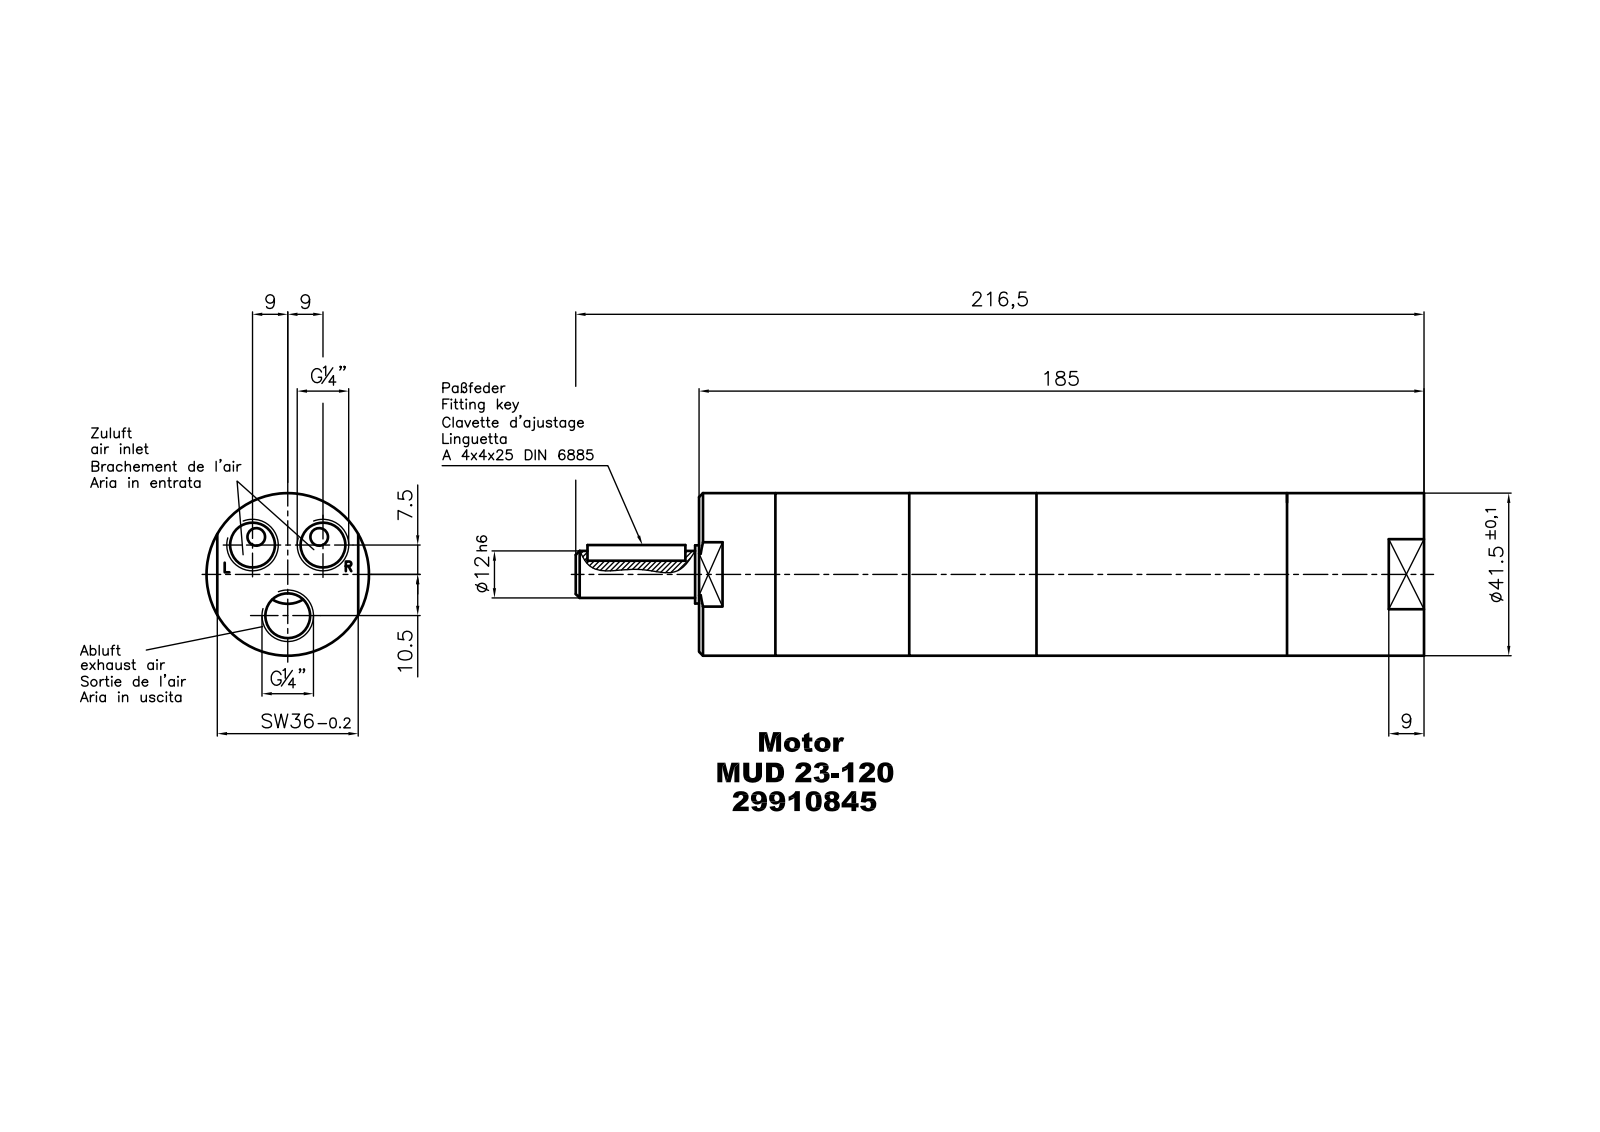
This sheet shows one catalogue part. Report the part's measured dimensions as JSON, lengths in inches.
{"part_name": "MUD 23-120_29910845", "step_written_by": "Autodesk Inventor 2008 (AUTOMOTIVE_DESIGN)", "units": "inches", "bodies": {"solids": 1, "faces": 329, "planar": 246, "cylindrical": 59, "other": 24}, "overall_size": [8.543, 1.634, 1.634], "volume_in3": 15.07, "surface_area_in2": 47.99, "round_holes": [[0.63, 1]], "round_bosses_or_shafts": [[1.634, 1], [1.417, 1], [0.589, 1], [0.472, 1]], "partial_cylinders_radius": [[0.009, 2], [0.01, 2], [0.011, 2], [0.011, 2], [0.013, 2], [0.022, 2], [0.033, 2], [0.036, 2]], "face_to_face_distances": [7.303, 1.496, 0.039, 0.02, 5.177, 5.197, 2.106, 2.126, 1.457, 1.417]}
